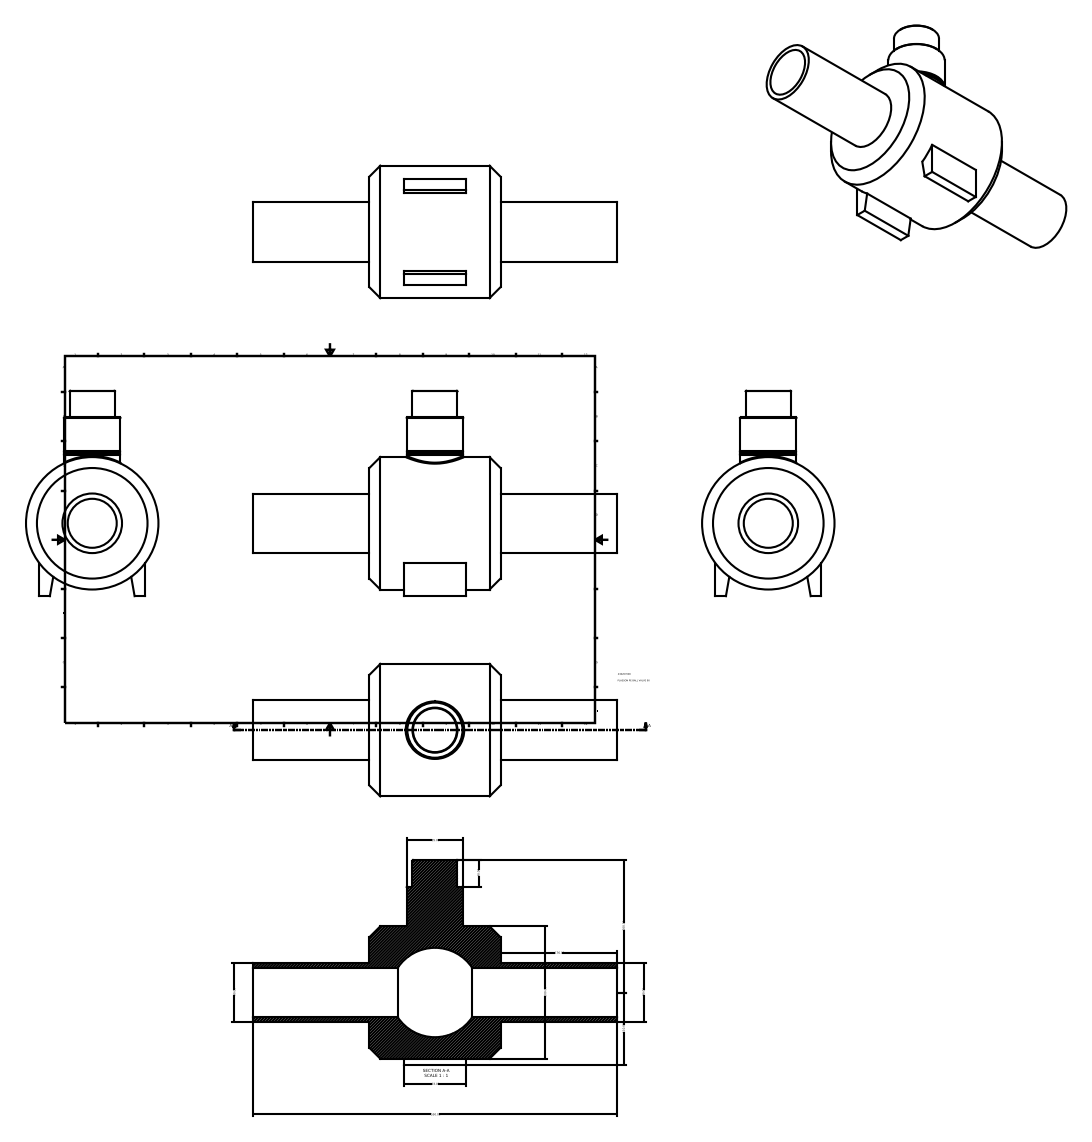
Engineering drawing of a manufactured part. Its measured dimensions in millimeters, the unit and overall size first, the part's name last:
Units: millimetres
Overall size (bounding box): 550 × 310 × 200
Round holes (diameter × count): ⌀74 ×1
Round bosses / shafts (diameter × count): ⌀200 ×1, ⌀90 ×1, ⌀85 ×1, ⌀68 ×1
Main face-to-face distances: 198, 160, 176, 374, 310, 228.5, 321.5, 52.5, 145.5, 550
Volume: 5 815 000 mm³ · Surface area: 455 825 mm²
Bodies: 1 solid, 33 faces (16 planar, 9 cylindrical, 8 other)
Part name (STEP PRODUCT): 436207090
STEP written by: Autodesk Inventor 2015 (AUTOMOTIVE_DESIGN)
